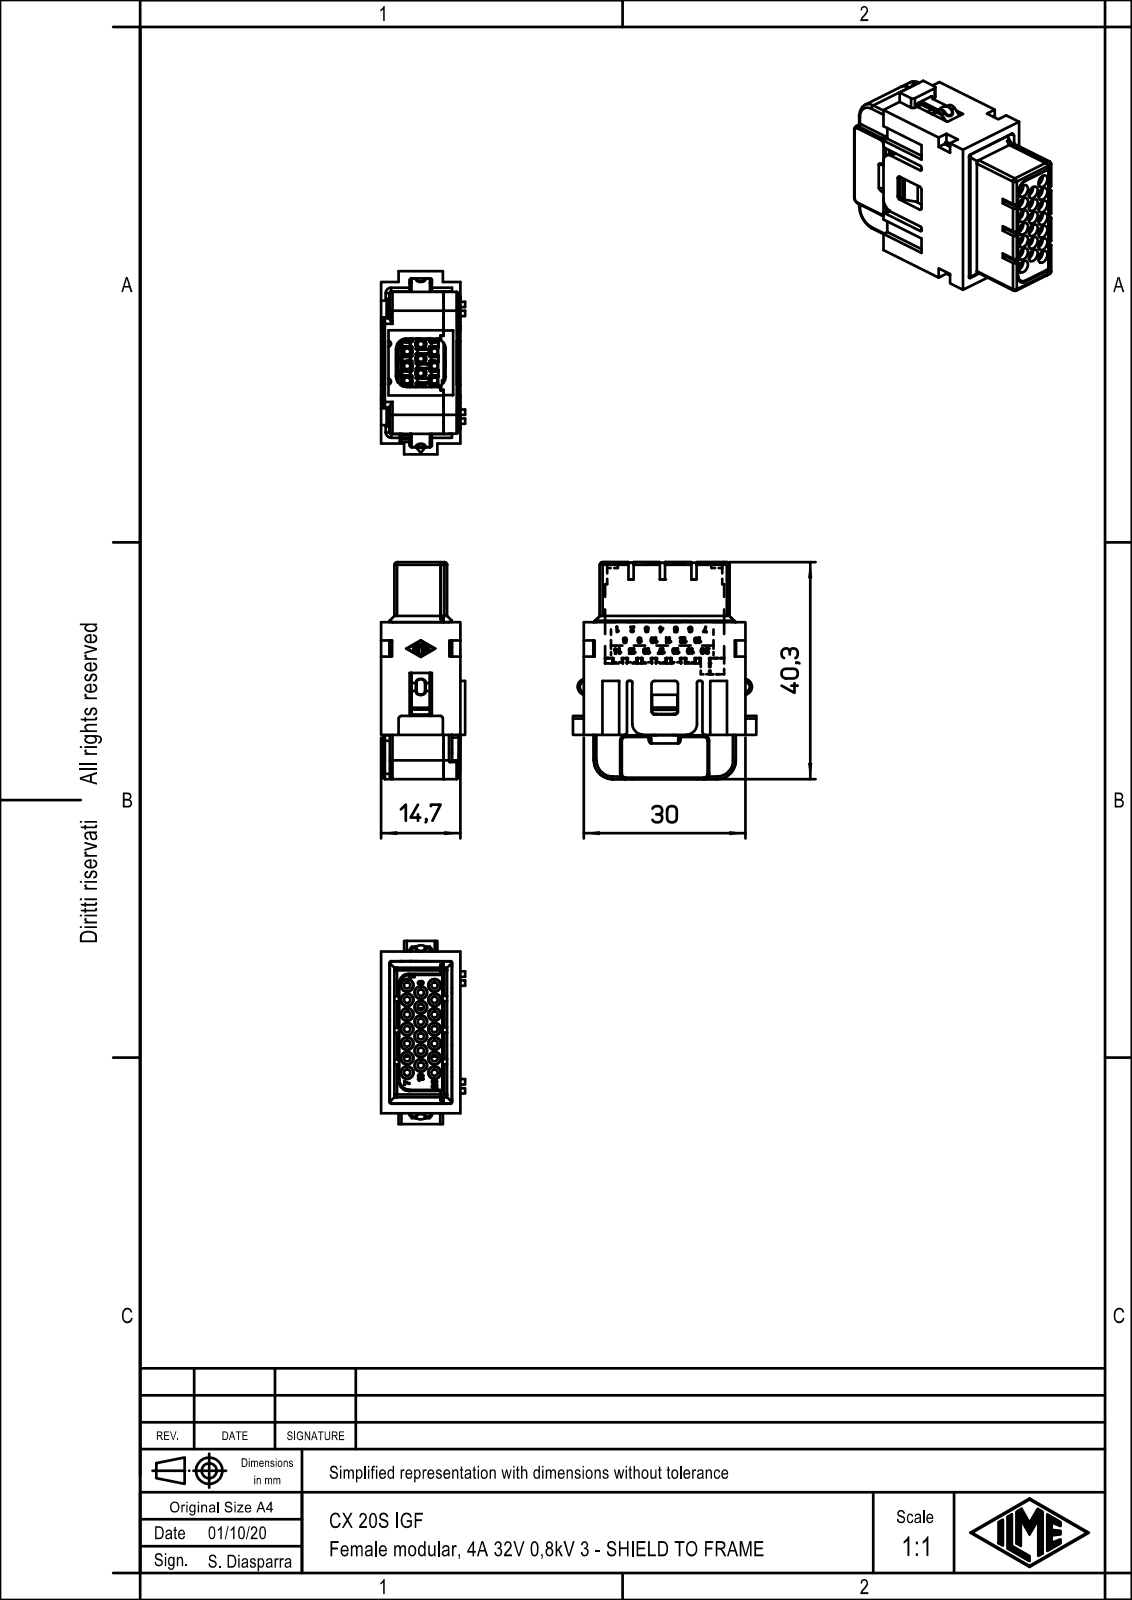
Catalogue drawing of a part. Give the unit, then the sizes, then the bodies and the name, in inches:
Units: inches
Overall size (bounding box): 1.587 × 1.339 × 0.614
Round holes (diameter × count): ⌀0.039 ×20, ⌀0.197 ×2
Round bosses / shafts (diameter × count): ⌀0.185 ×2
Partial cylindrical surfaces — rounded edges, fillets, slot ends (radius × count): R0.012 ×21, R0.02 ×19, R0.039 ×6, R0.045 ×2, R0.071 ×2, R0.073 ×2, R0.094 ×2, R0.138 ×2
Main face-to-face distances: 0.13, 0.449, 0.033, 0.457, 0.327, 0.132, 0.317, 0.325, 0.122, 0.579
Hole centre spacings: 0.114, 0.189, 0.106, 0.284, 0.213, 0.227, 0.385, 0.319
Volume: 0.638 in³ · Surface area: 14.25 in²
Bodies: 1 solid, 426 faces (268 planar, 116 cylindrical, 42 other)
Part name (STEP PRODUCT): CX_20S_IGF
STEP written by: Creo Elements/Direct Modeling 20.1B 02-Apr-2019 (C) Parametric Technology GmbH (AUTOMOTIVE_DESIGN)
